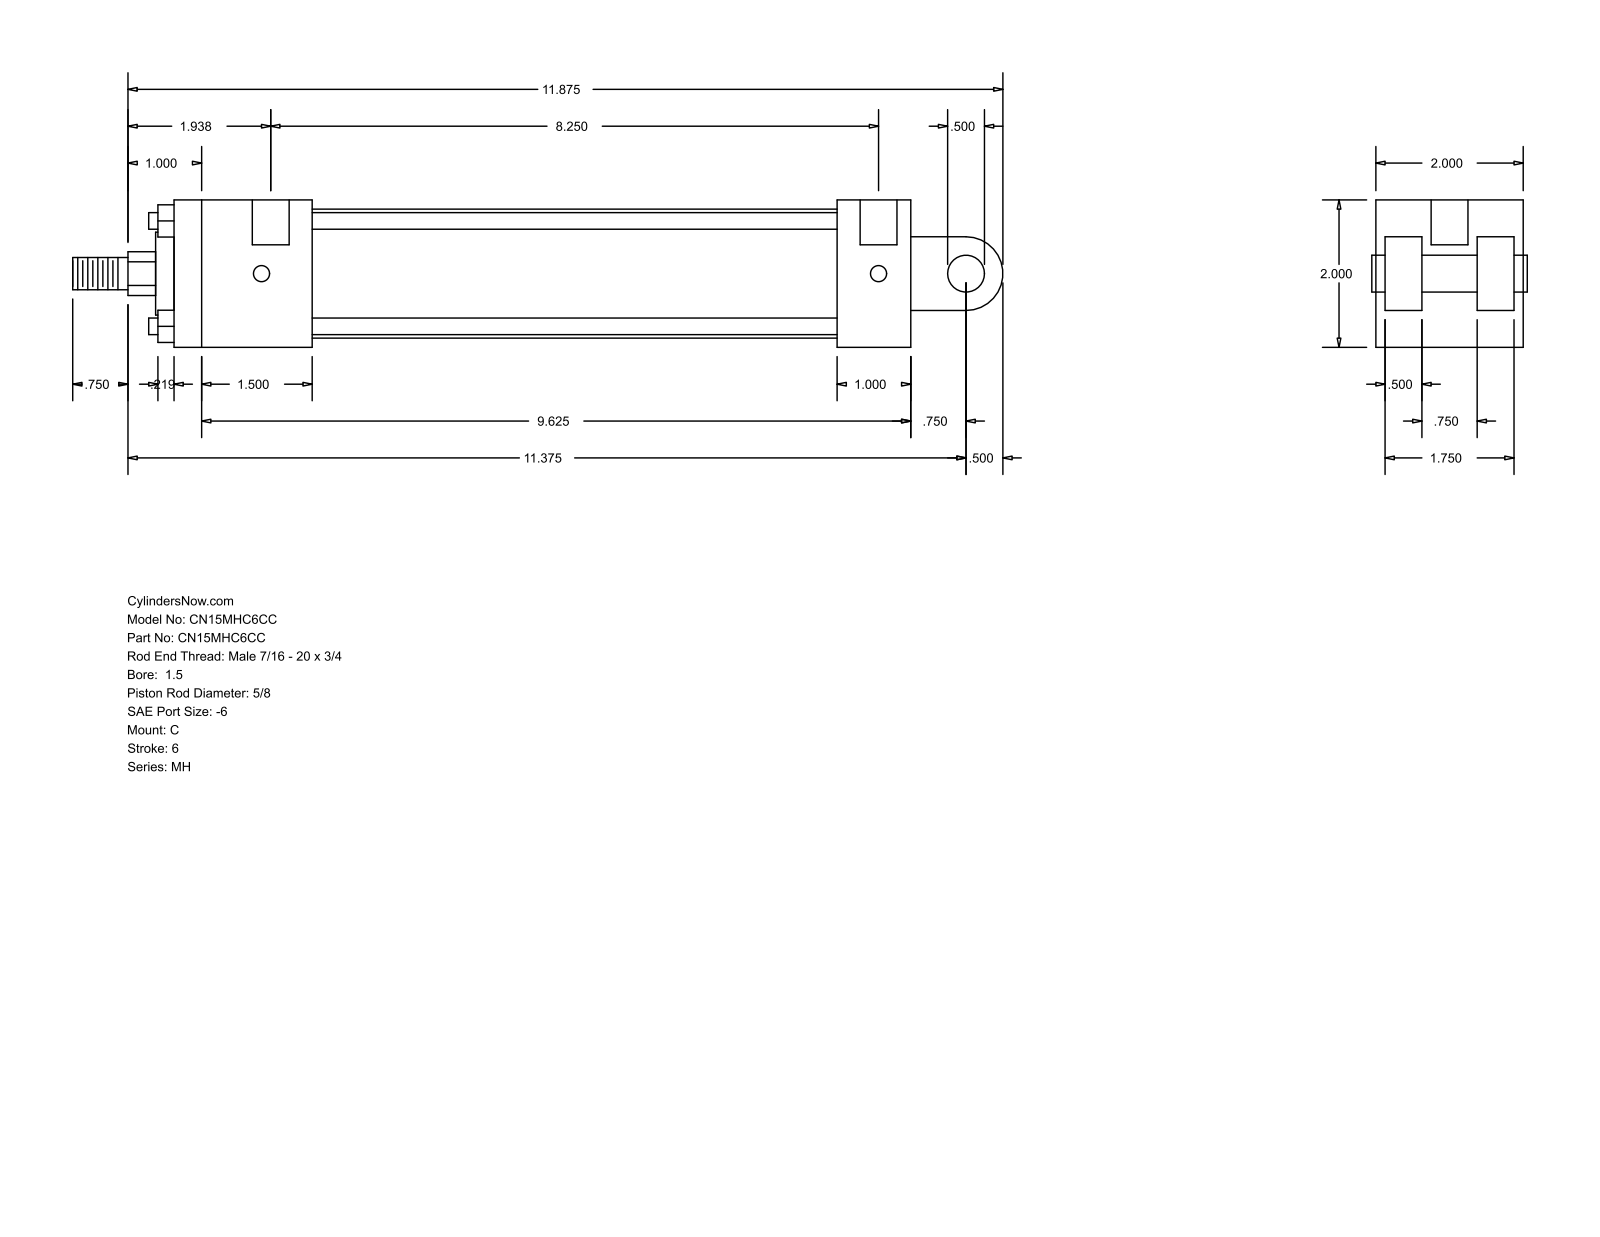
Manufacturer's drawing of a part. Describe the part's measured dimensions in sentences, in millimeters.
The part is named "MH_C__0150_0.625". Its 3-D file was written by "GSSL Pune (CONFIG_CONTROL_DESIGN)". It is 0 solids with 99 faces: 70 planar, 29 cylindrical and 0 other. Overall it measures 320.68 by 50.8 by 50.8 millimeters. Round holes: 4 of diameter 5.56, 2 of diameter 12.7. Round bosses or shafts: 4 of diameter 5.71, 1 of diameter 44.45, 1 of diameter 28.57, 1 of diameter 15.88, 1 of diameter 12.7, 1 of diameter 11.11. Partial cylindrical surfaces (rounded edges, fillets, slot ends): 1 of radius 7.54, 1 of radius 12.7. The main face-to-face distances are 50.8, 12.7, 254, 34.93, 3.17, 15.87, 47.63, 31.76, 38.1, 47.62. The hole center spacings are 212.72, 3.17, 209.55.
